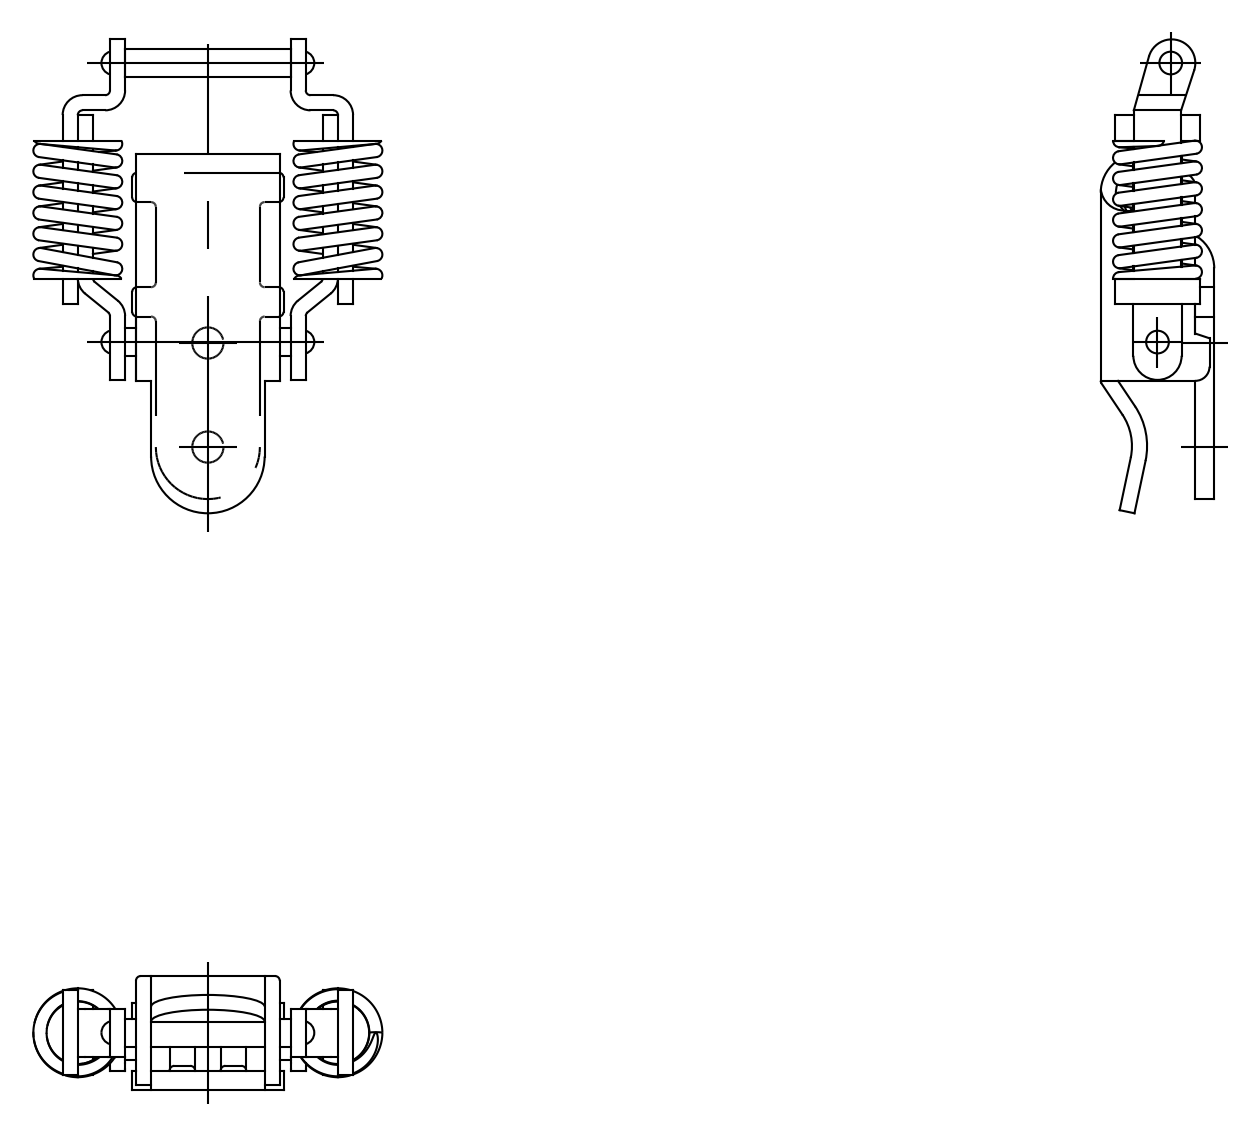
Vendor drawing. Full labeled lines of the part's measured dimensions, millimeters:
Part name (STEP PRODUCT): spring; arm_AB; arm_C; base (+1 more)
STEP written by: spGate 18.9.1 (****-****-****-****) (AUTOMOTIVE_DESIGN)
Units: millimetres
Bodies: 6 solids, 385 faces (130 planar, 103 cylindrical, 152 other)
Overall size (bounding box): 50.1 × 36.9 × 12
Volume: 4 143 mm³ · Surface area: 6 940 mm²
Round holes (diameter × count): ⌀3.3 ×2, ⌀3.2 ×1
Round bosses / shafts (diameter × count): ⌀3 ×2
Partial cylindrical surfaces — rounded edges, fillets, slot ends (radius × count): R0.5 ×45, R2.1 ×8, R1.5 ×3, R2 ×3, R2.5 ×3, R3.6 ×2, R4.1 ×2, R6 ×2
Main face-to-face distances: 1.6, 21.35, 6.15, 7.75, 19.75, 12, 27.5, 2, 13.6, 10
Hole centre spacings: 11
